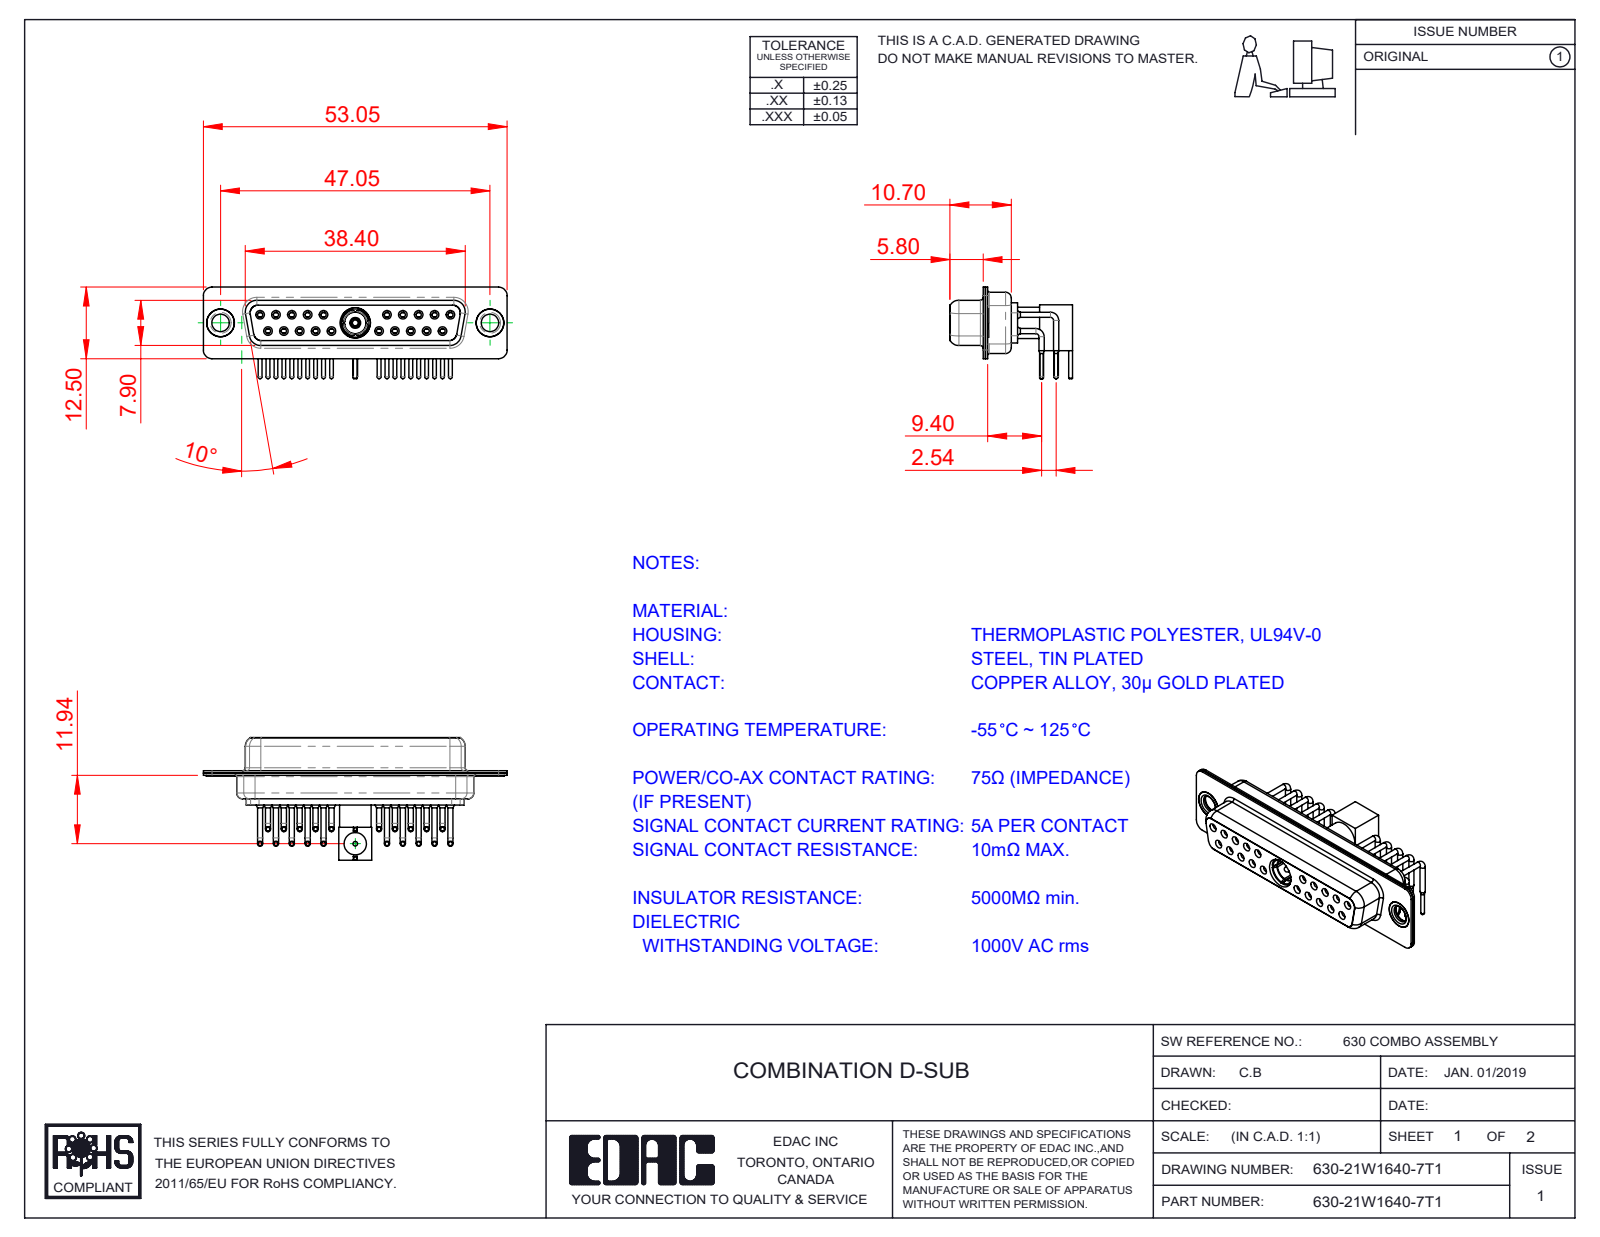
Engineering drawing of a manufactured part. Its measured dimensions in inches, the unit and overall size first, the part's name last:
Units: inches
Overall size (bounding box): 2.089 × 0.843 × 0.63
Round holes (diameter × count): ⌀0.043 ×21, ⌀0.059 ×21, ⌀0.035 ×20, ⌀0.079 ×20, ⌀0.063 ×10, ⌀0.067 ×10, ⌀0.191 ×3, ⌀0.12 ×2, ⌀0.157 ×2, ⌀0.159 ×2, ⌀0.031 ×1, ⌀0.111 ×1
Round bosses / shafts (diameter × count): ⌀0.035 ×20, ⌀0.026 ×20, ⌀0.063 ×10, ⌀0.197 ×3, ⌀0.195 ×2, ⌀0.189 ×2, ⌀0.14 ×2, ⌀0.217 ×1
Partial cylindrical surfaces — rounded edges, fillets, slot ends (radius × count): R0.059 ×16, R0.079 ×12, R0.053 ×8, R0.063 ×8, R0.01 ×4, R0.02 ×4, R0.024 ×4, R0.026 ×4
Main face-to-face distances: 0.016, 0.018, 0.055, 0.333, 0.071, 0.35, 0.244, 0.278, 0.073, 0.335
Hole centre spacings: 0.124, 0.109, 0.218, 0.327, 0.198, 0.763, 0.826, 0.872
Volume: 0.251 in³ · Surface area: 15.23 in²
Bodies: 31 solids, 1481 faces (434 planar, 646 cylindrical, 401 other)
Part name (STEP PRODUCT): Co-Ax Plug_RA PC Tail; 630Combo Contact Row 1; 630Combo Shell Front_25 Contacts; 630Combo Contact Row 2 (+8 more)
STEP written by: SolidWorks 2020 (CONFIG_CONTROL_DESIGN)
